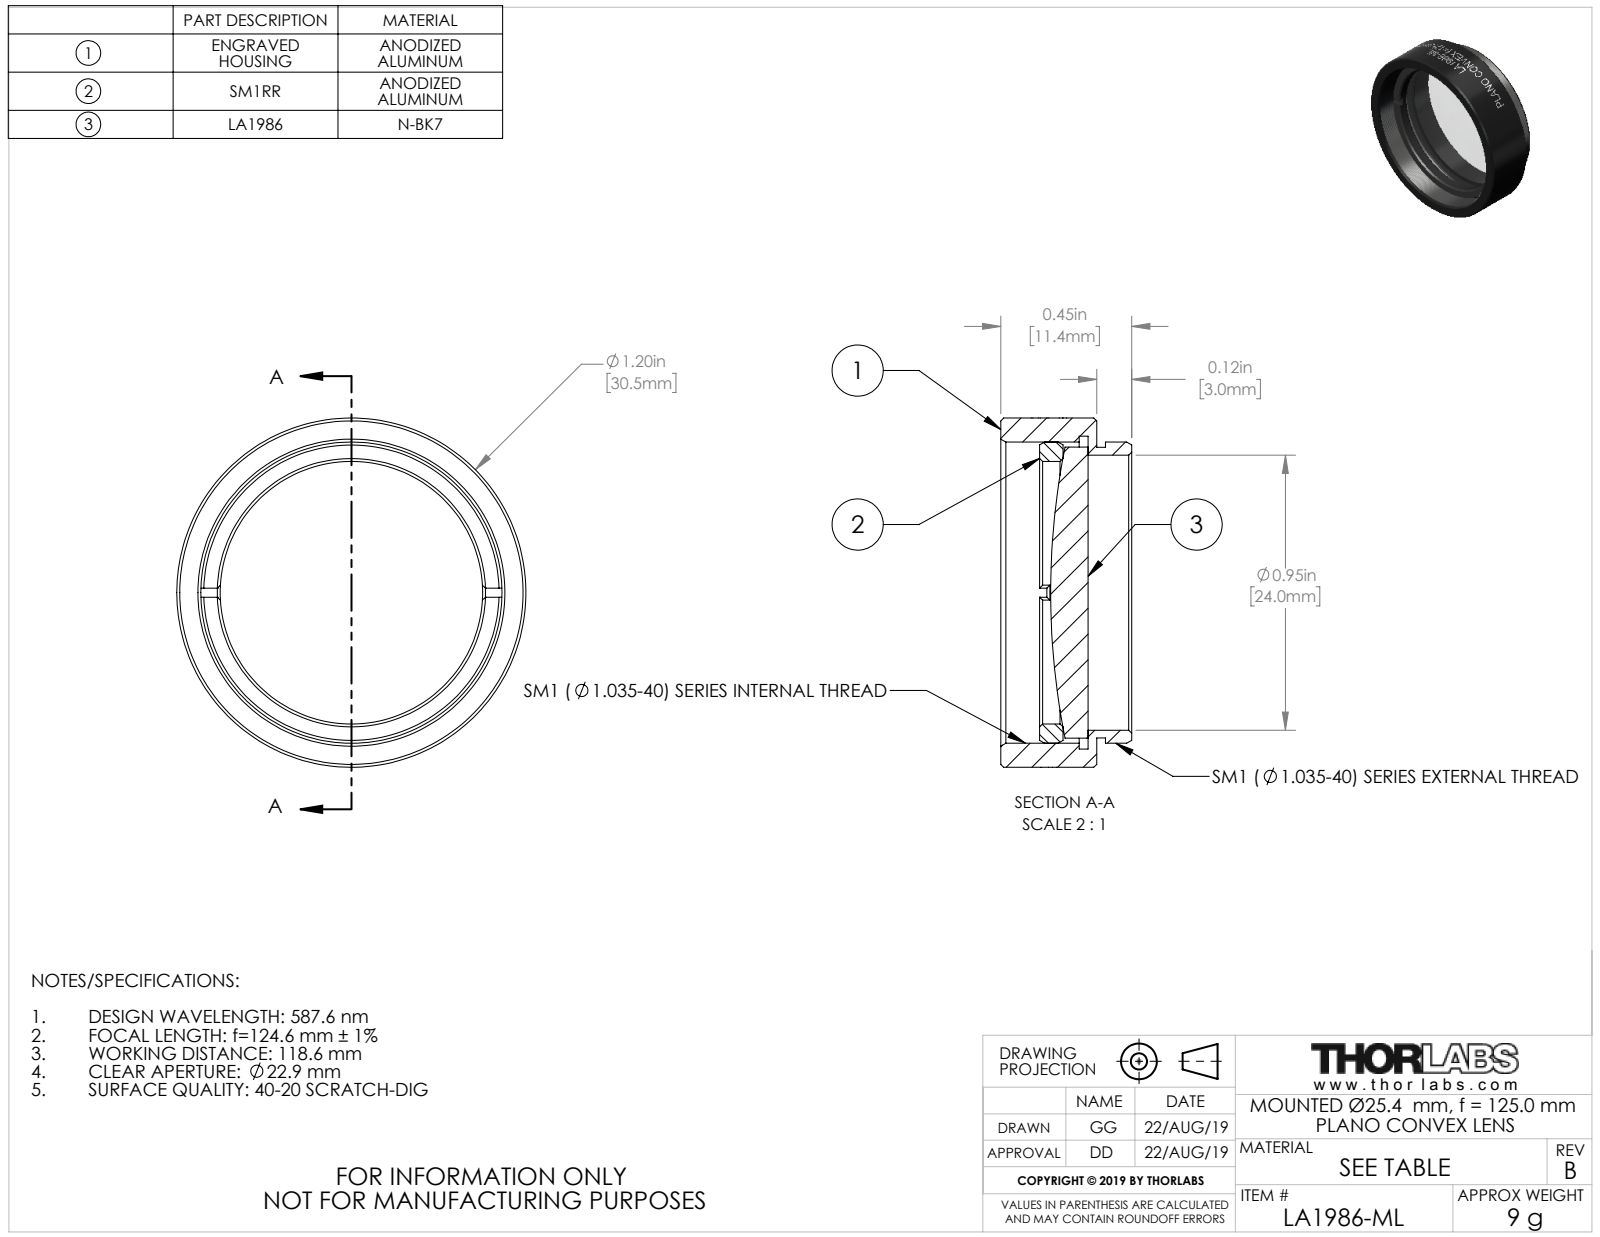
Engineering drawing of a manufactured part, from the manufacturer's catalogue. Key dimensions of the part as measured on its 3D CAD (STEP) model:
Part name (STEP PRODUCT): 24442-E0W
STEP written by: SolidWorks 2018 (CONFIG_CONTROL_DESIGN)
Units: millimetres
Bodies: 3 solids, 119 faces (20 planar, 75 cylindrical, 24 other)
Overall size (bounding box): 30.48 × 30.48 × 11.43
Volume: 3 414 mm³ · Surface area: 4 317 mm²
Round holes (diameter × count): ⌀22.91 ×1, ⌀24 ×1, ⌀27.3 ×1
Round bosses / shafts (diameter × count): ⌀30.48 ×1, ⌀26.29 ×1, ⌀25.4 ×1, ⌀25.37 ×1
Main face-to-face distances: 0.76, 8.38, 7.62, 2.95, 2.19, 5.43, 4.98, 4.22, 2.03, 3.4
